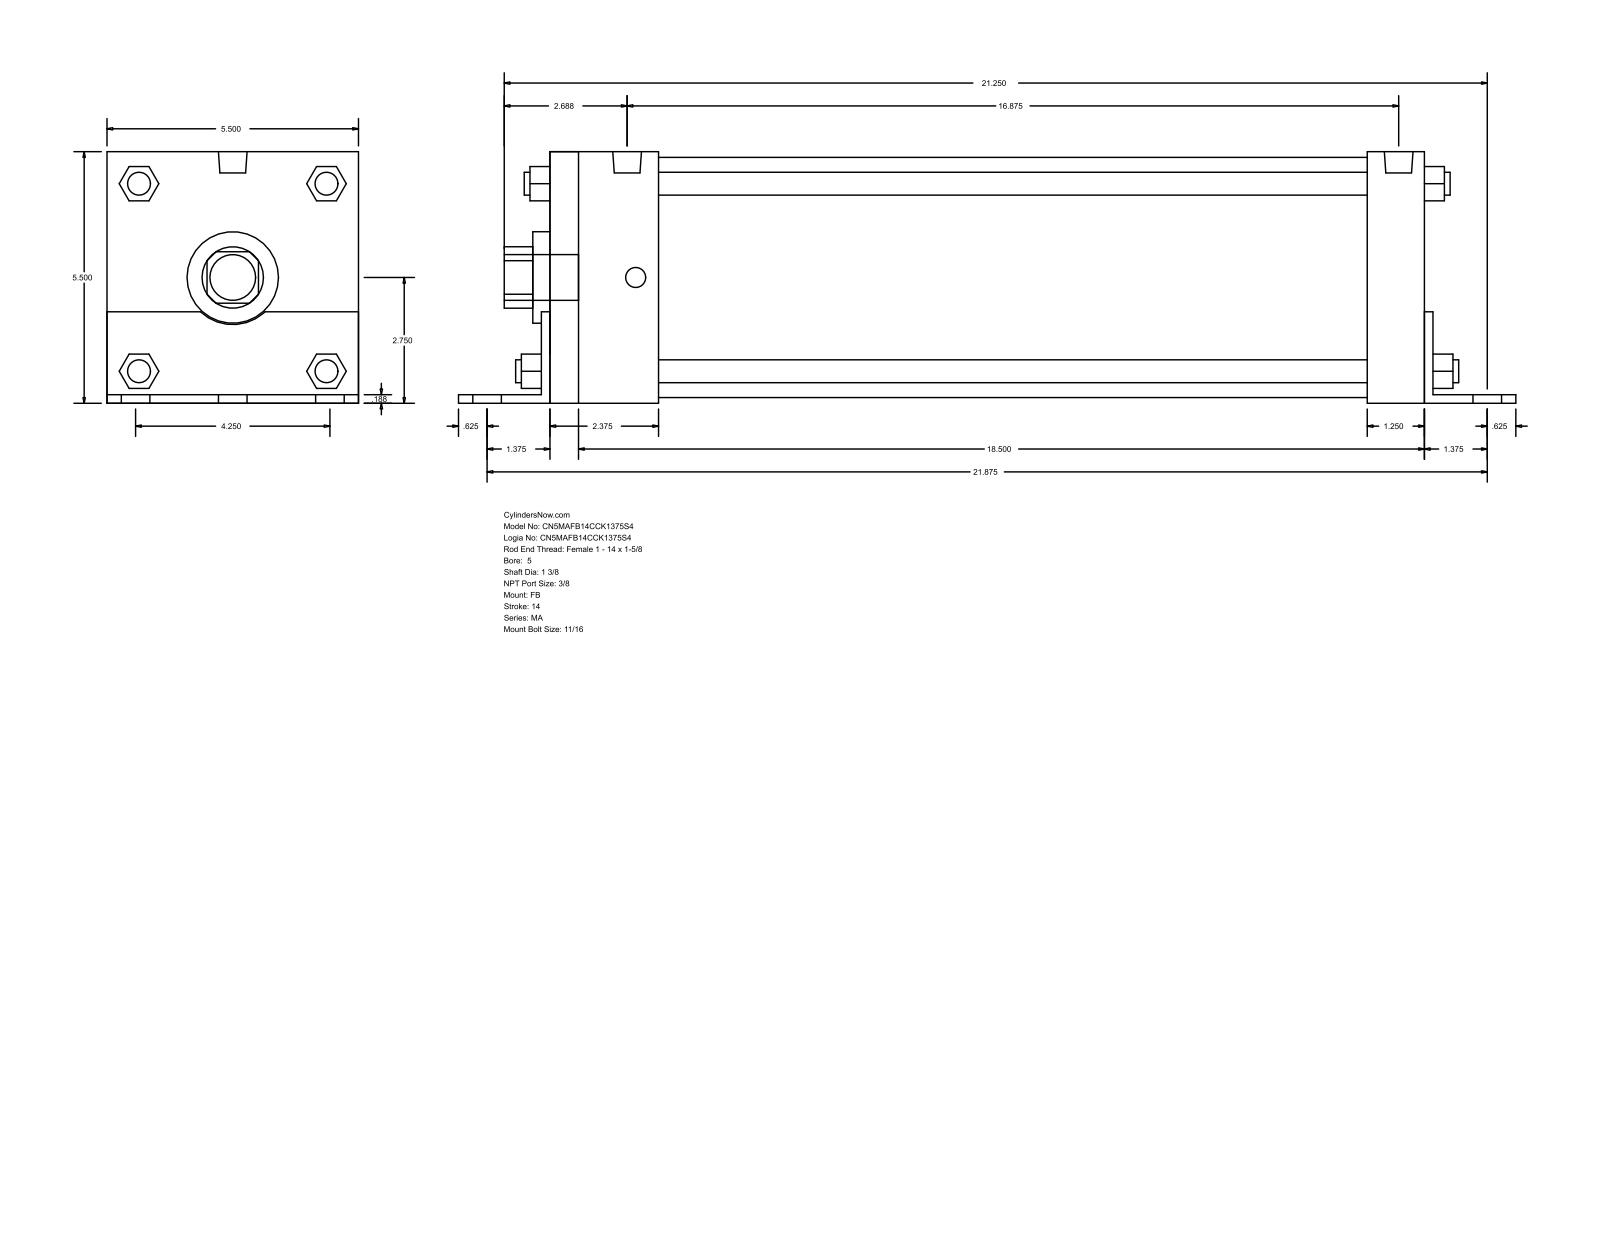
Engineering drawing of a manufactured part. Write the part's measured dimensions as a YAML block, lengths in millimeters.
part_name: "MA_FB__0500_1.375"
step_written_by: "GSSL Pune (CONFIG_CONTROL_DESIGN)"
units: millimeters
bodies: {solids: 0, faces: 140, planar: 105, cylindrical: 35, other: 0}
overall_size: [587.38, 139.75, 139.7]
round_holes:
  - {diameter: 34.92, count: 1}
  - {diameter: 50.8, count: 1}
  - {diameter: 133.35, count: 1}
round_bosses_or_shafts:
  - {diameter: 17.46, count: 6}
  - {diameter: 12.7, count: 4}
  - {diameter: 11.11, count: 4}
  - {diameter: 15.93, count: 2}
  - {diameter: 25.4, count: 1}
partial_cylinders:
  - {radius: 17.06, count: 1}
  - {radius: 26.16, count: 1}
face_to_face_distances: [139.7, 4.76, 139.75, 490.54, 4.71, 134.99, 485.78, 495.3, 31.75, 36.51]
